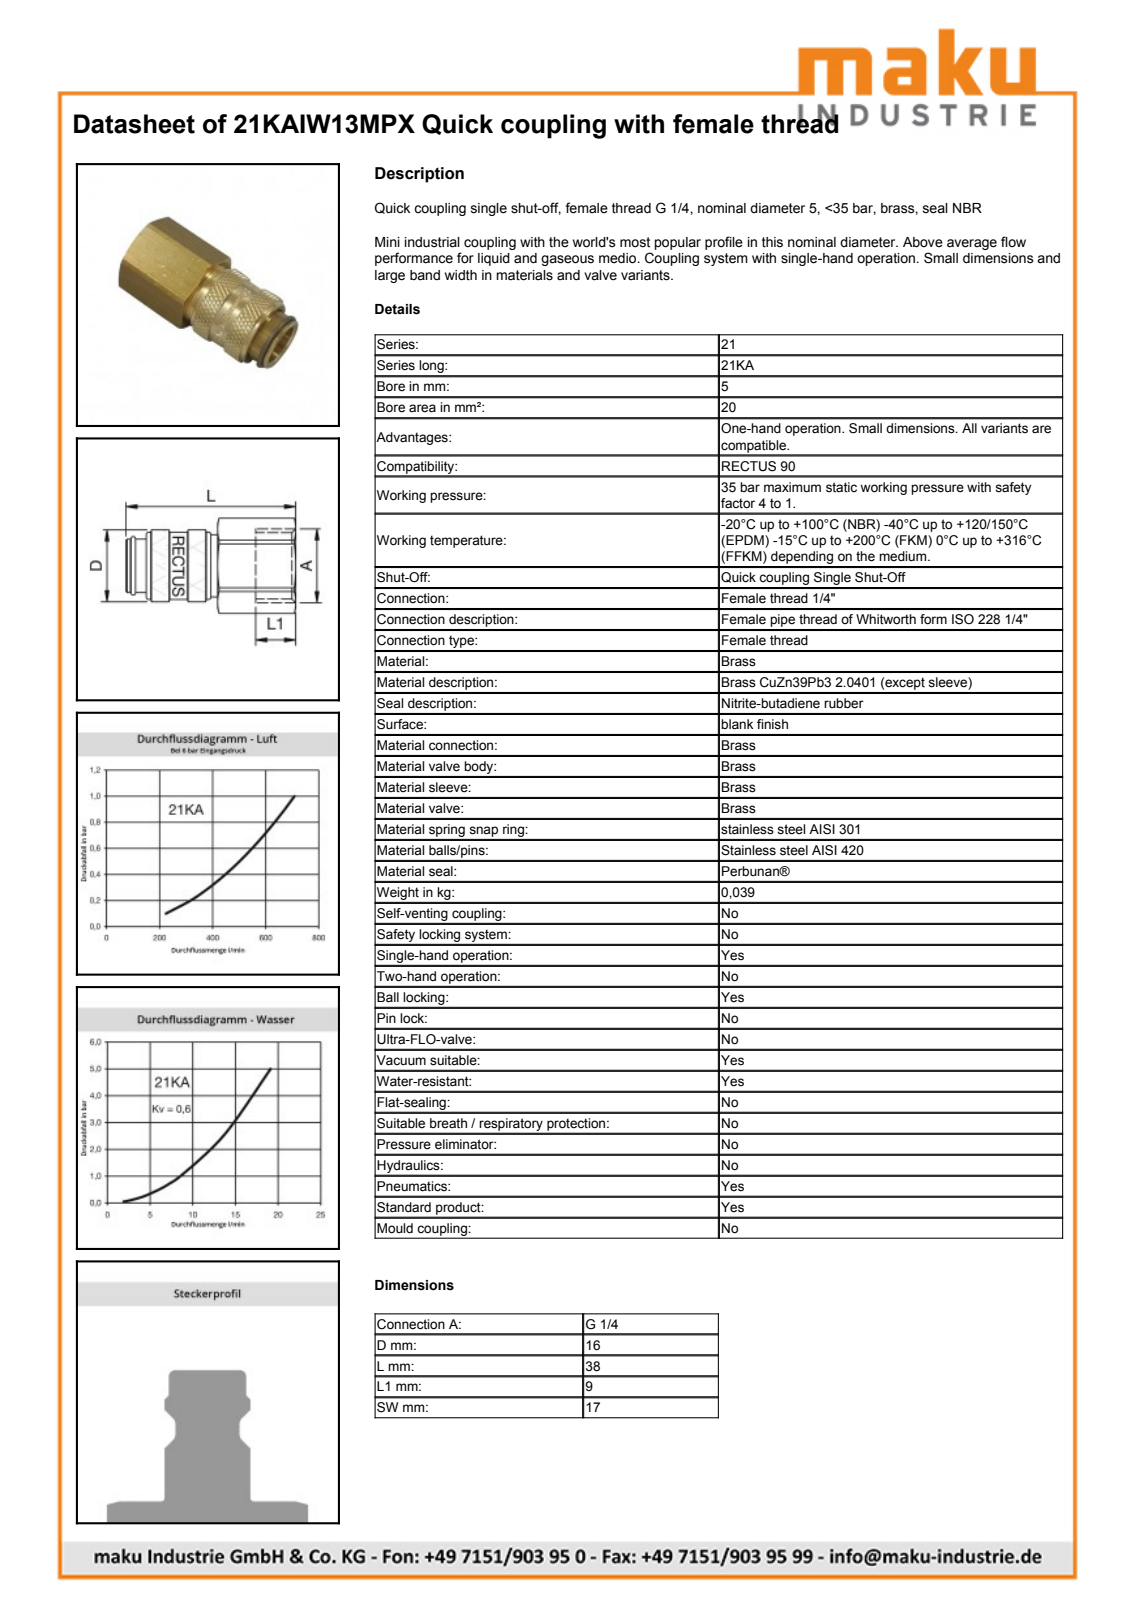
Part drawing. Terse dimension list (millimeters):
name: D107127
written by: Autodesk Inventor 2013 (AUTOMOTIVE_DESIGN)
unit: mm
bodies: 2 solids, 452 faces (148 planar, 60 cylindrical, 244 other)
size: 38.15 × 18.93 × 18.4
volume: 6 629 mm³; area: 4 160 mm²
holes: 1× ⌀10.7, 1× ⌀11.45, 1× ⌀12.15, 1× ⌀14
bosses: 1× ⌀16.15, 1× ⌀15.1, 1× ⌀12, 1× ⌀11.15, 1× ⌀10.3
rounds: 1× R7.45, 1× R9.57
face distances: 17, 29.16, 38.15, 8.99, 4.45, 8.56, 20.6, 17.55, 16.15, 13.01
